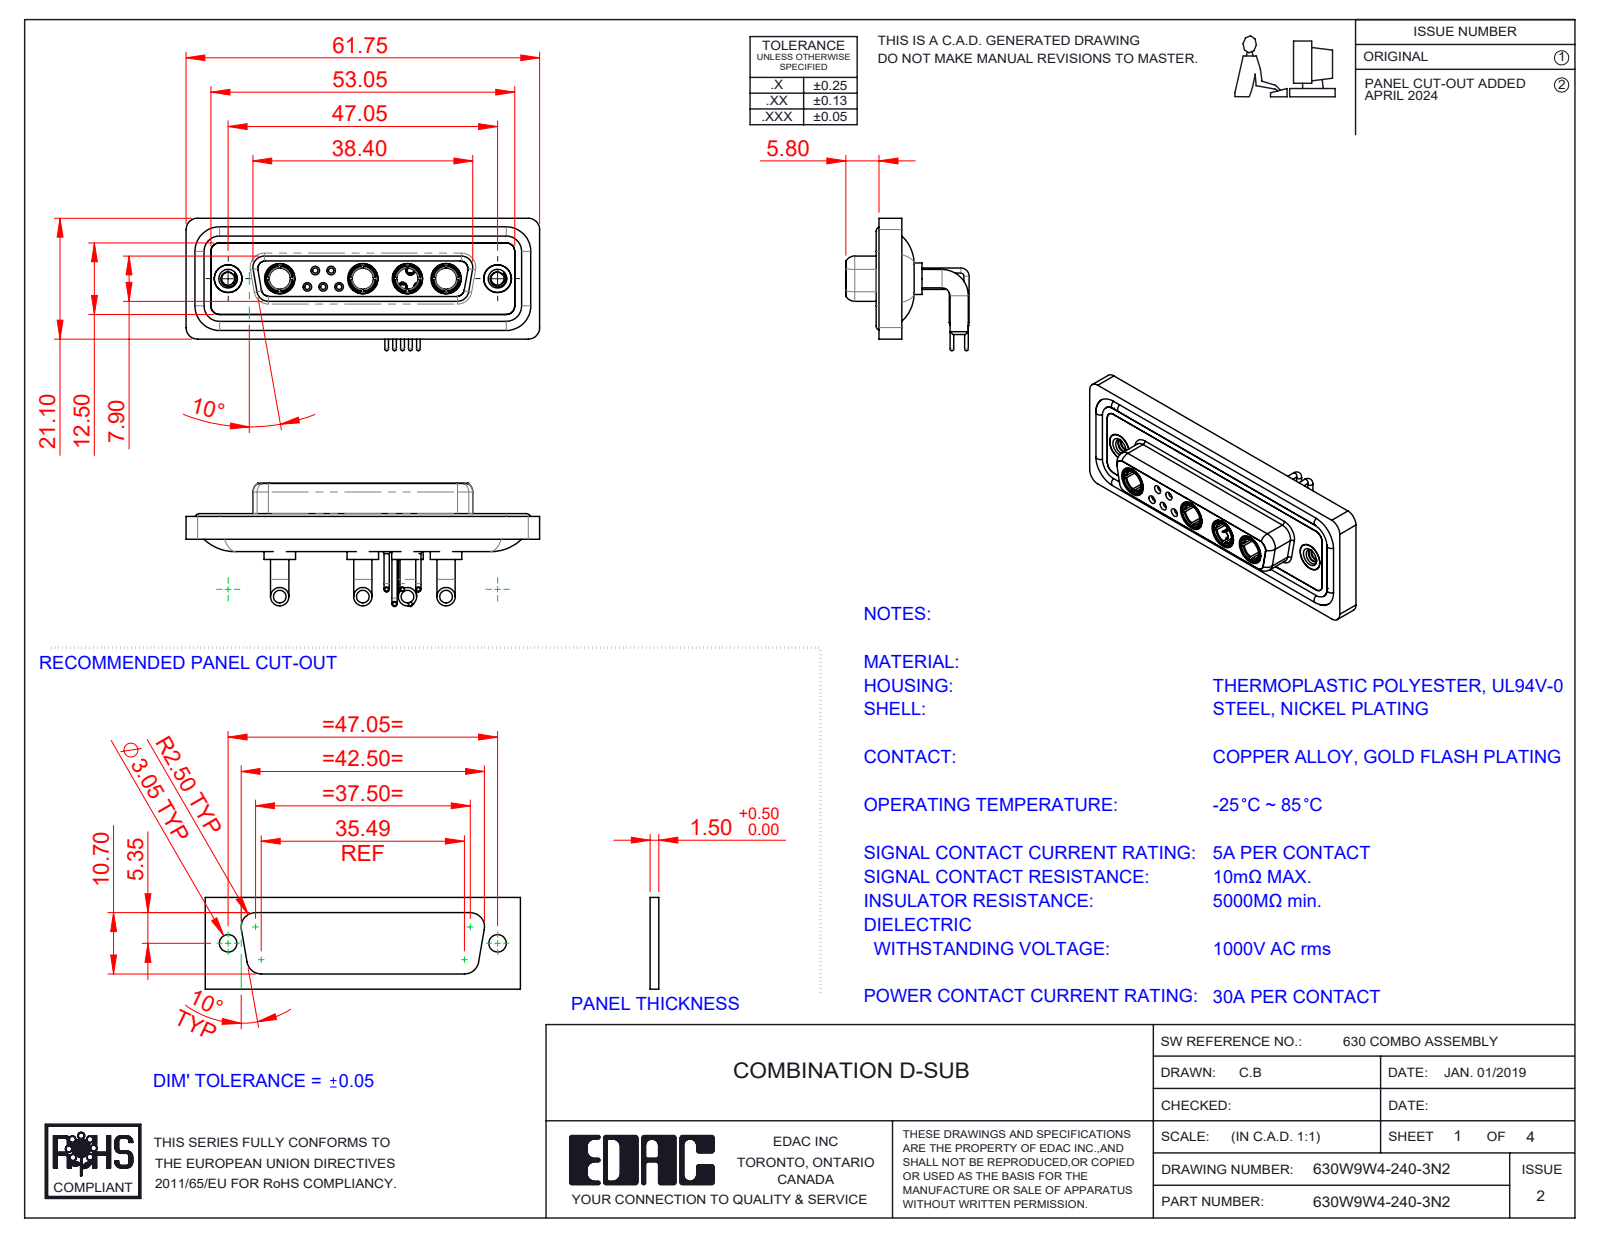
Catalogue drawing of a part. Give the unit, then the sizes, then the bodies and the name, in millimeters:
Units: millimetres
Overall size (bounding box): 61.75 × 23.12 × 21.53
Round holes (diameter × count): ⌀4.85 ×6, ⌀0.9 ×5, ⌀1.1 ×5, ⌀1.5 ×5, ⌀2 ×5, ⌀3.7 ×4, ⌀5.3 ×4, ⌀1.6 ×3, ⌀1.7 ×2, ⌀2.26 ×2, ⌀4 ×2, ⌀4.05 ×2
Round bosses / shafts (diameter × count): ⌀0.9 ×10, ⌀1.6 ×9, ⌀3.2 ×8, ⌀2 ×5, ⌀1.5 ×5, ⌀0.65 ×5, ⌀5.5 ×4, ⌀5.2 ×4
Partial cylindrical surfaces — rounded edges, fillets, slot ends (radius × count): R1.5 ×18, R2 ×18, R1.35 ×8, R1.6 ×8, R0.25 ×4, R0.5 ×4, R0.6 ×4, R0.65 ×4
Main face-to-face distances: 0.4, 1.8, 4.1, 1.1, 1.6, 1.5, 2.5, 3.1, 3.7, 1.4
Hole centre spacings: 3.16, 2.77, 5.04, 13.85, 11.08, 12.79, 15.5, 5.54
Volume: 8 563 mm³ · Surface area: 14 120 mm²
Bodies: 20 solids, 963 faces (296 planar, 403 cylindrical, 264 other)
Part name (STEP PRODUCT): 630W9W4-140-3N2; Power Socket_30A RA; 630Combo Shell Front_25 Contacts; 630Combo Contact Row 1_50 Contacts (+5 more)
STEP written by: SolidWorks 2023 (CONFIG_CONTROL_DESIGN)
